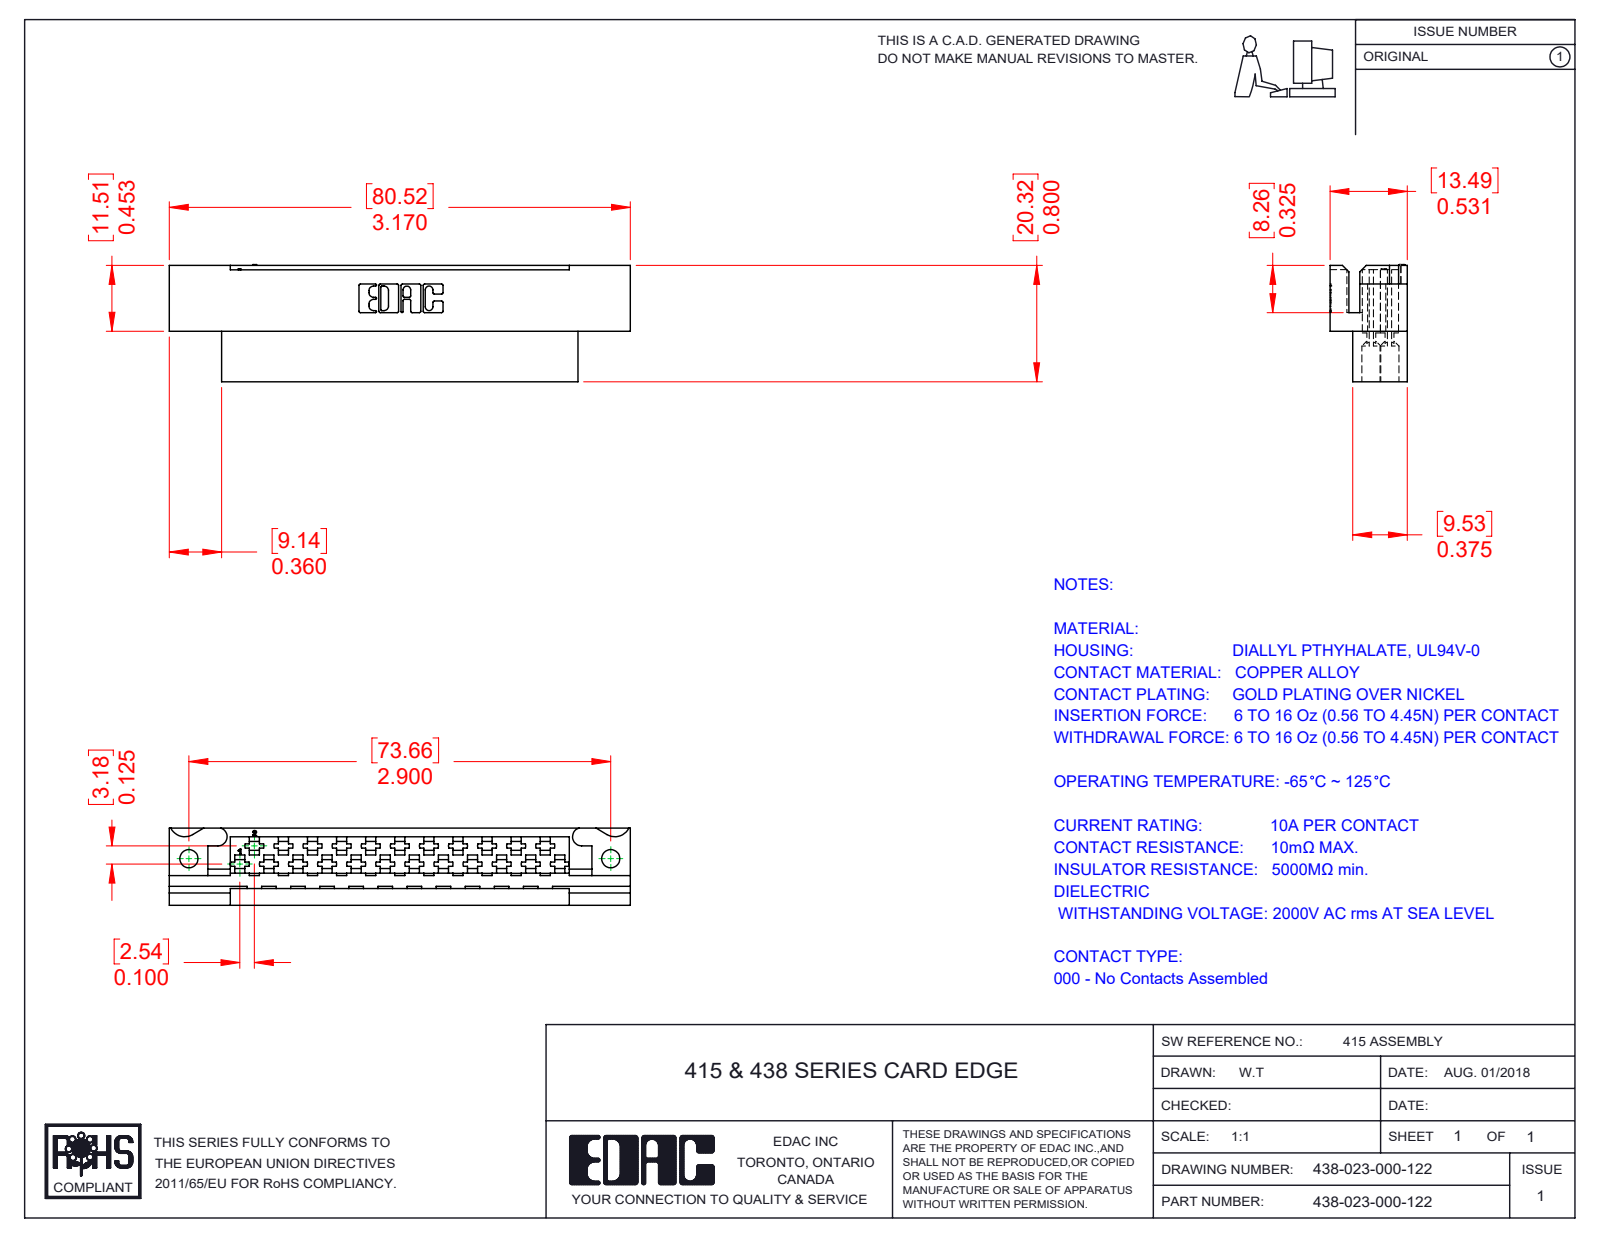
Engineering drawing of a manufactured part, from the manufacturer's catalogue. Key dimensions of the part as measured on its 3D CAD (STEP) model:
Part name (STEP PRODUCT): 438-023-000-122; 438-210-001_438-210-023-112
STEP written by: SolidWorks 2016 (CONFIG_CONTROL_DESIGN)
Units: millimetres
Bodies: 1 solid, 754 faces (567 planar, 96 cylindrical, 91 other)
Overall size (bounding box): 80.52 × 20.45 × 13.49
Volume: 12 112 mm³ · Surface area: 11 747 mm²
Round holes (diameter × count): ⌀3.3 ×23, ⌀3.17 ×1, ⌀3.18 ×1
Partial cylindrical surfaces — rounded edges, fillets, slot ends (radius × count): R0.25 ×22, R0.17 ×6, R0.8 ×6, R0.67 ×3, R1.59 ×2, R2.7 ×2
Main face-to-face distances: 13.49, 9.53, 3.96, 3.18, 3.17, 1.23, 4.38, 1.2, 5.12, 0.74
Hole centre spacings: 4.06, 5.08, 8.25, 10.16, 13.09, 15.24, 18.06, 20.32
